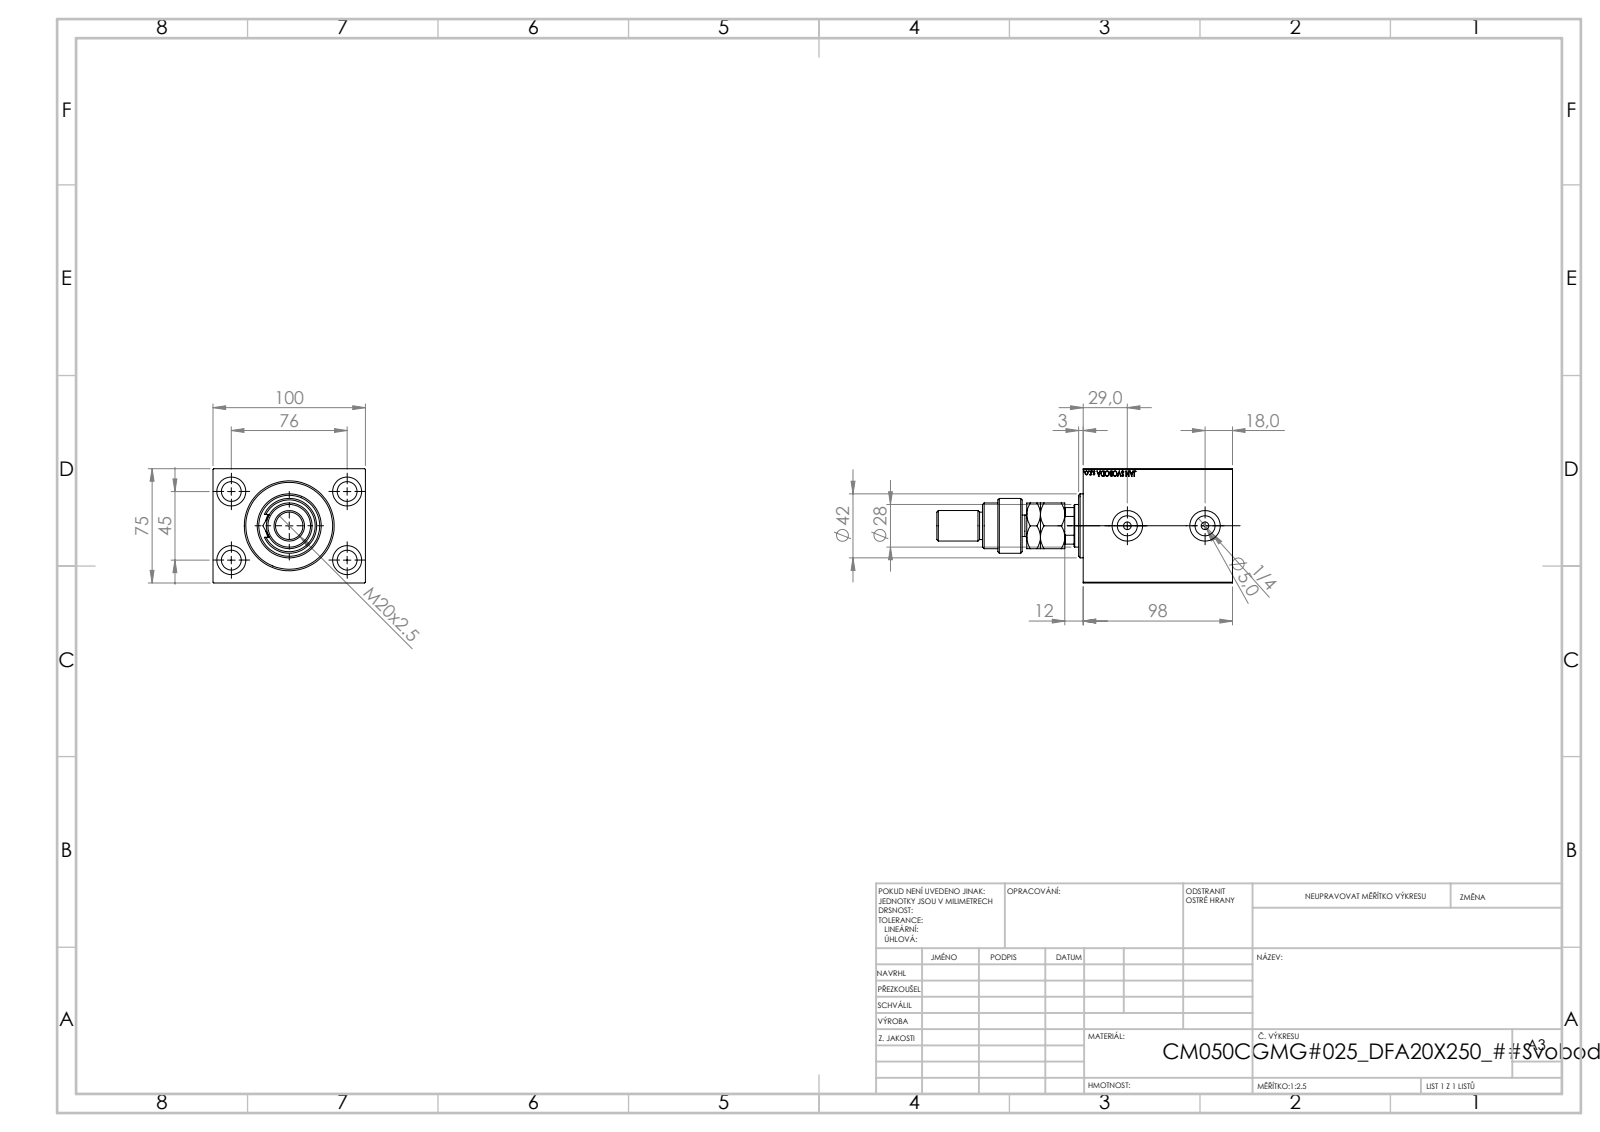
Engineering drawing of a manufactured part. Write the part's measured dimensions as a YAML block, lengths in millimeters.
part_name: "V450CM_VC_B; FEMALE_PART_FOR_DFA; V450CM_C_Body; V450CM_C_VCP (+1 more)"
step_written_by: "SolidWorks 2019 (CONFIG_CONTROL_DESIGN)"
units: millimeters
bodies: {solids: 5, faces: 950, planar: 437, cylindrical: 75, other: 438}
overall_size: [194, 100, 75]
volume: 679839
surface_area: 118733
round_holes:
  - {diameter: 13, count: 4}
  - {diameter: 19, count: 4}
  - {diameter: 5, count: 2}
  - {diameter: 13.16, count: 2}
  - {diameter: 20, count: 2}
  - {diameter: 18.5, count: 1}
  - {diameter: 28, count: 1}
  - {diameter: 31.5, count: 1}
  - {diameter: 50, count: 1}
  - {diameter: 52, count: 1}
  - {diameter: 57, count: 1}
round_bosses_or_shafts:
  - {diameter: 42, count: 1}
  - {diameter: 36, count: 1}
  - {diameter: 30, count: 1}
  - {diameter: 22, count: 1}
  - {diameter: 20, count: 1}
  - {diameter: 18, count: 1}
  - {diameter: 14, count: 1}
partial_cylinders:
  - {radius: 7.5, count: 1}
  - {radius: 12, count: 1}
  - {radius: 13.5, count: 1}
face_to_face_distances: [75, 100, 98, 84, 14, 12, 25, 37, 72, 30]
hole_center_spacings: [44.16, 45, 76, 88.32, 51]
